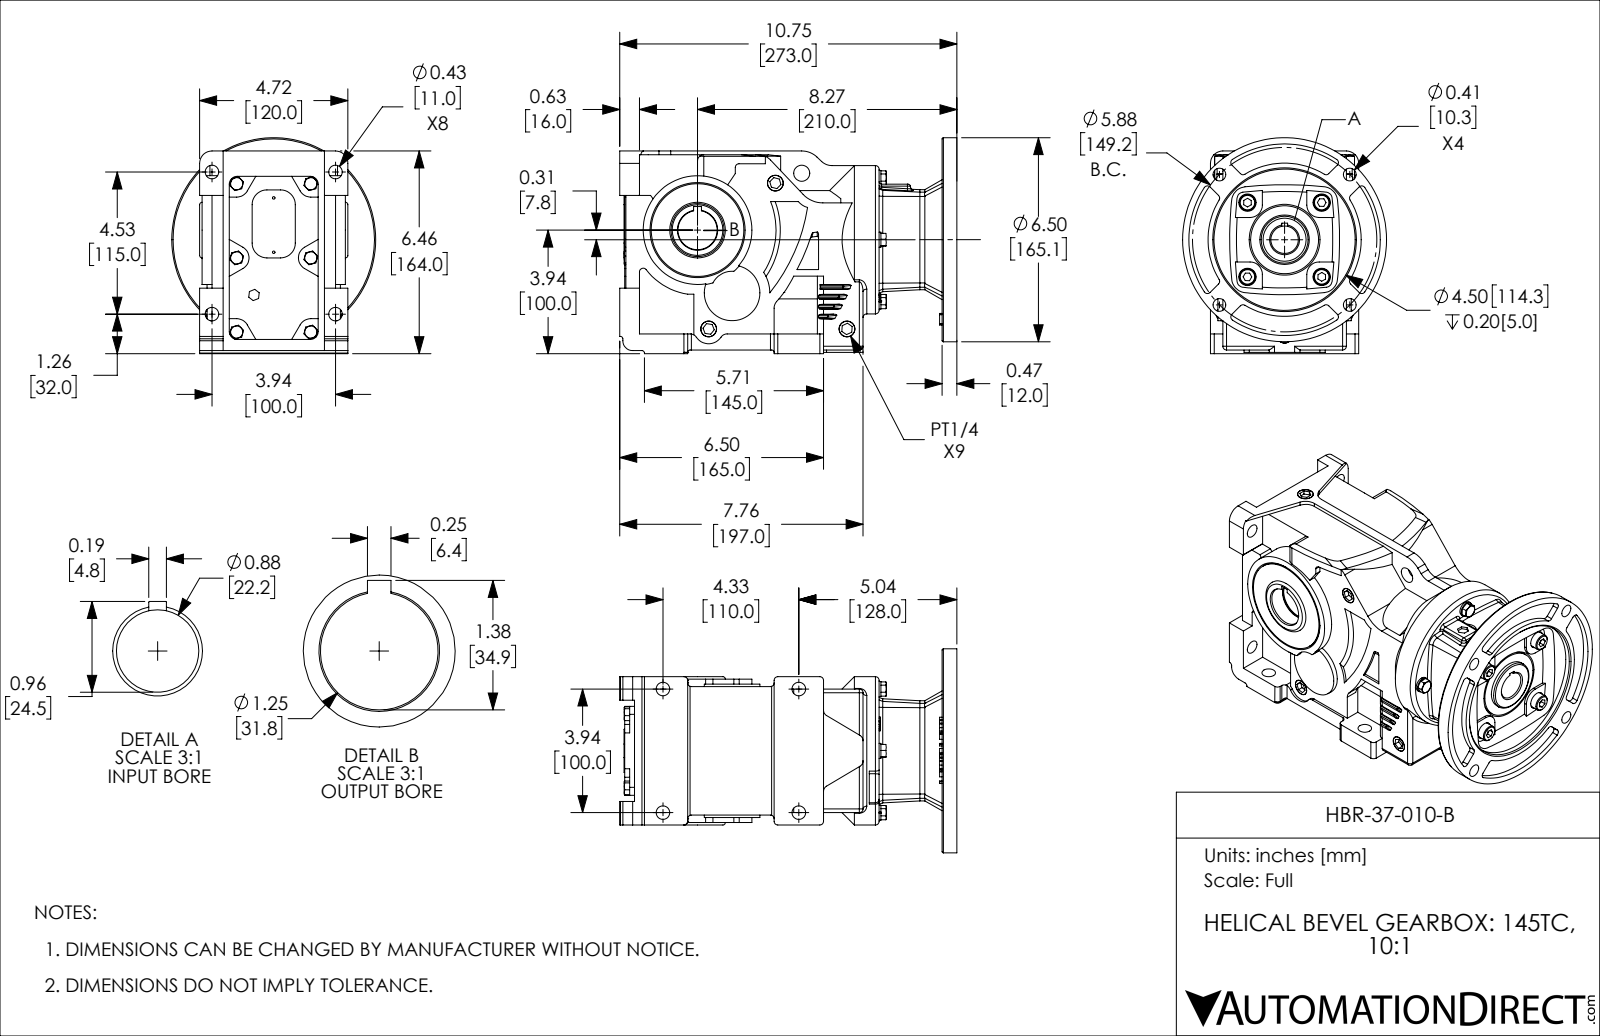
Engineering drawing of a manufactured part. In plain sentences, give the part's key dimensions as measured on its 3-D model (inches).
The part is named "HBR-37-010-B". Its 3-D file was written by "SolidWorks 2018 (AUTOMOTIVE_DESIGN)". It is 1 solid with 1103 faces: 542 planar, 292 cylindrical and 269 other. Overall it measures 10.748 by 6.88 by 6.5 inches. Its volume is 210.9 cubic inches and its surface area 395.6 square inches. Round holes: 8 of diameter 0.433, 4 of diameter 0.24, 4 of diameter 0.276, 4 of diameter 0.406, 4 of diameter 0.551, 2 of diameter 0.079, 1 of diameter 0.512, 1 of diameter 0.875, 1 of diameter 1.25, 1 of diameter 1.327, 1 of diameter 4.5. Round bosses or shafts: 4 of diameter 0.512, 4 of diameter 0.48, 4 of diameter 0.236, 1 of diameter 6.5, 1 of diameter 4.724, 1 of diameter 3.465, 1 of diameter 2.953, 1 of diameter 2.165. Partial cylindrical surfaces (rounded edges, fillets, slot ends): 38 of radius 0.118, 18 of radius 0.039, 14 of radius 0.394, 11 of radius 0.197, 10 of radius 0.079, 6 of radius 0.472, 4 of radius 0.157, 4 of radius 0.256. The main face-to-face distances are 0.472, 0.315, 0.118, 0.157, 0.079, 4.252, 0.276, 0.394, 3.937, 0.512. The hole center spacings are 2.08, 4.548, 3.937, 1.42, 1.673, 1.969, 2.784, 2.937.
